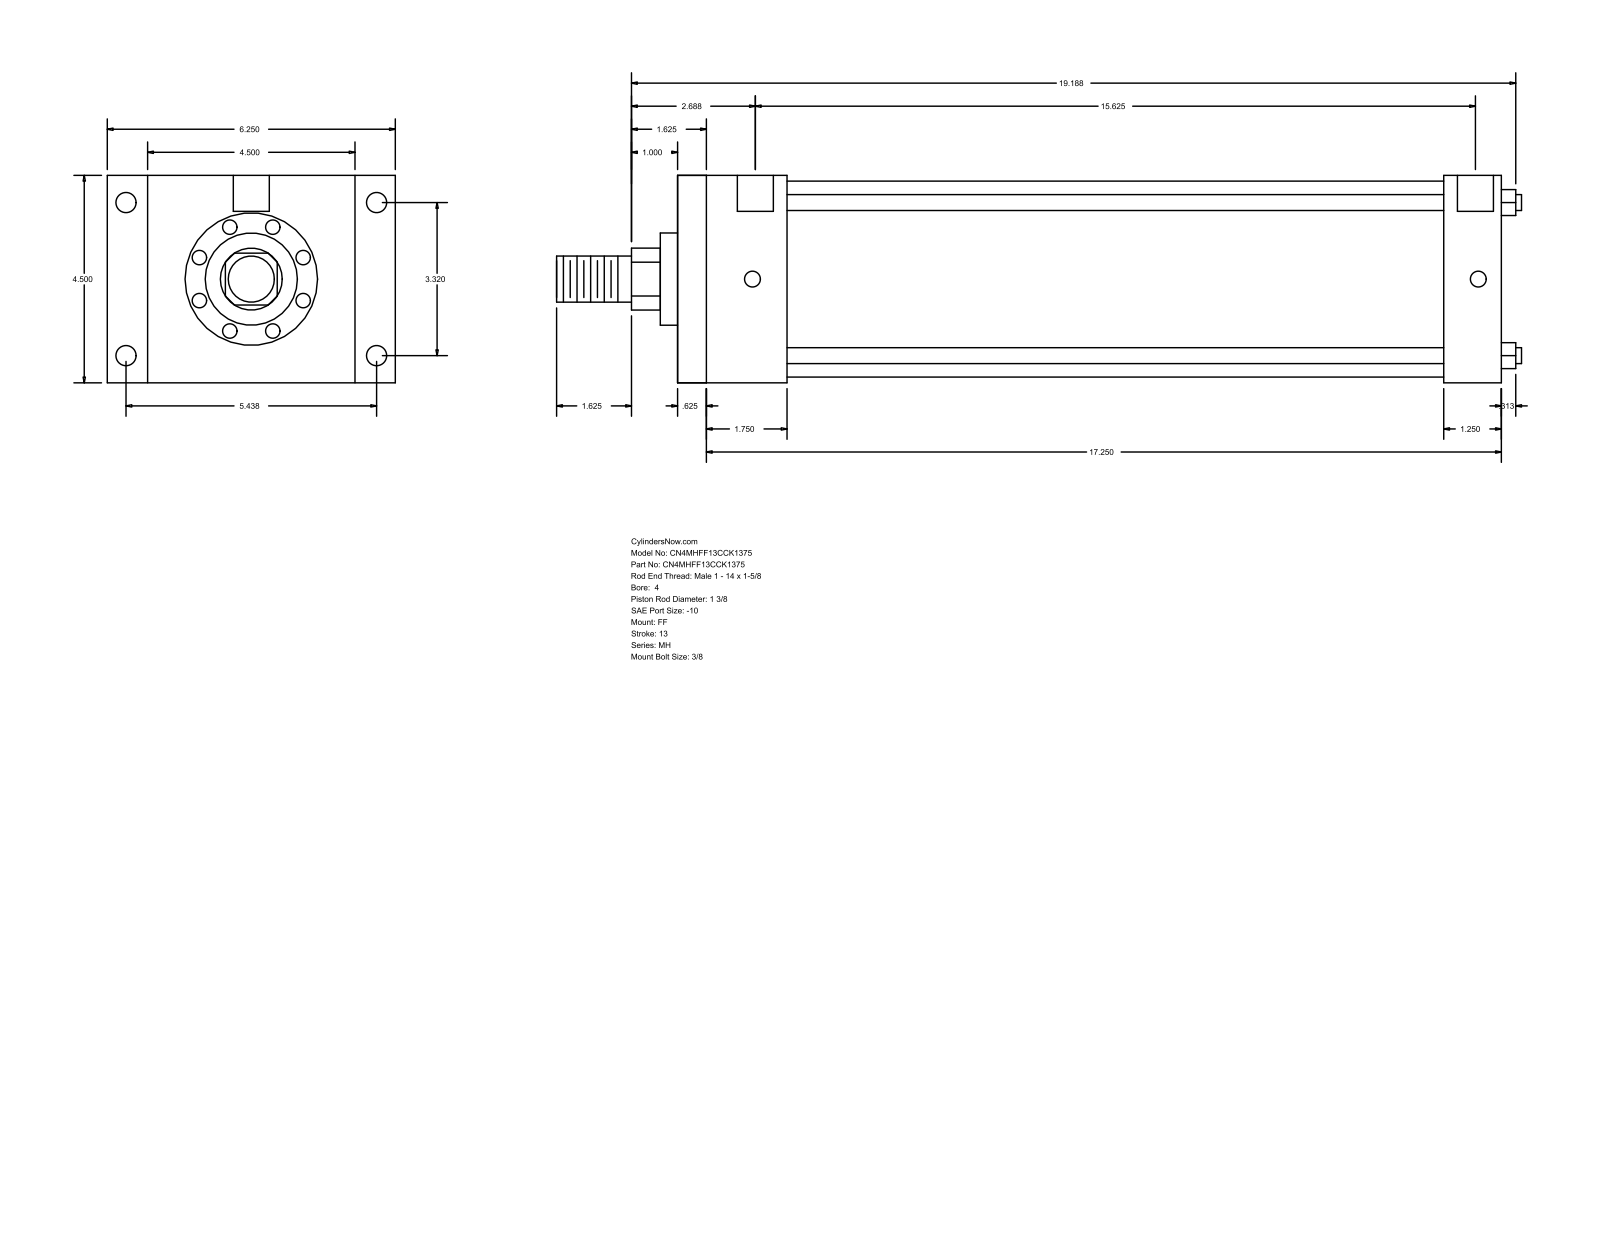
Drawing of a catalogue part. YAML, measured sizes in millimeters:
part_name: "MH_FF__0400_1.375"
step_written_by: "GSSL Pune (CONFIG_CONTROL_DESIGN)"
units: millimeters
bodies: {solids: 0, faces: 92, planar: 64, cylindrical: 28, other: 0}
overall_size: [531.81, 158.75, 114.3]
round_holes:
  - {diameter: 8.73, count: 4}
  - {diameter: 11.13, count: 4}
  - {diameter: 19.84, count: 2}
round_bosses_or_shafts:
  - {diameter: 8.76, count: 4}
  - {diameter: 107.95, count: 1}
  - {diameter: 50.8, count: 1}
  - {diameter: 34.92, count: 1}
  - {diameter: 25.4, count: 1}
partial_cylinders:
  - {radius: 17.06, count: 1}
face_to_face_distances: [114.3, 454.03, 15.87, 438.16, 60.32, 44.45, 393.71, 422.28, 406.41, 361.96]
hole_center_spacings: [1.59, 84.32, 138.12, 161.82, 398.47, 400.06, 396.88]
